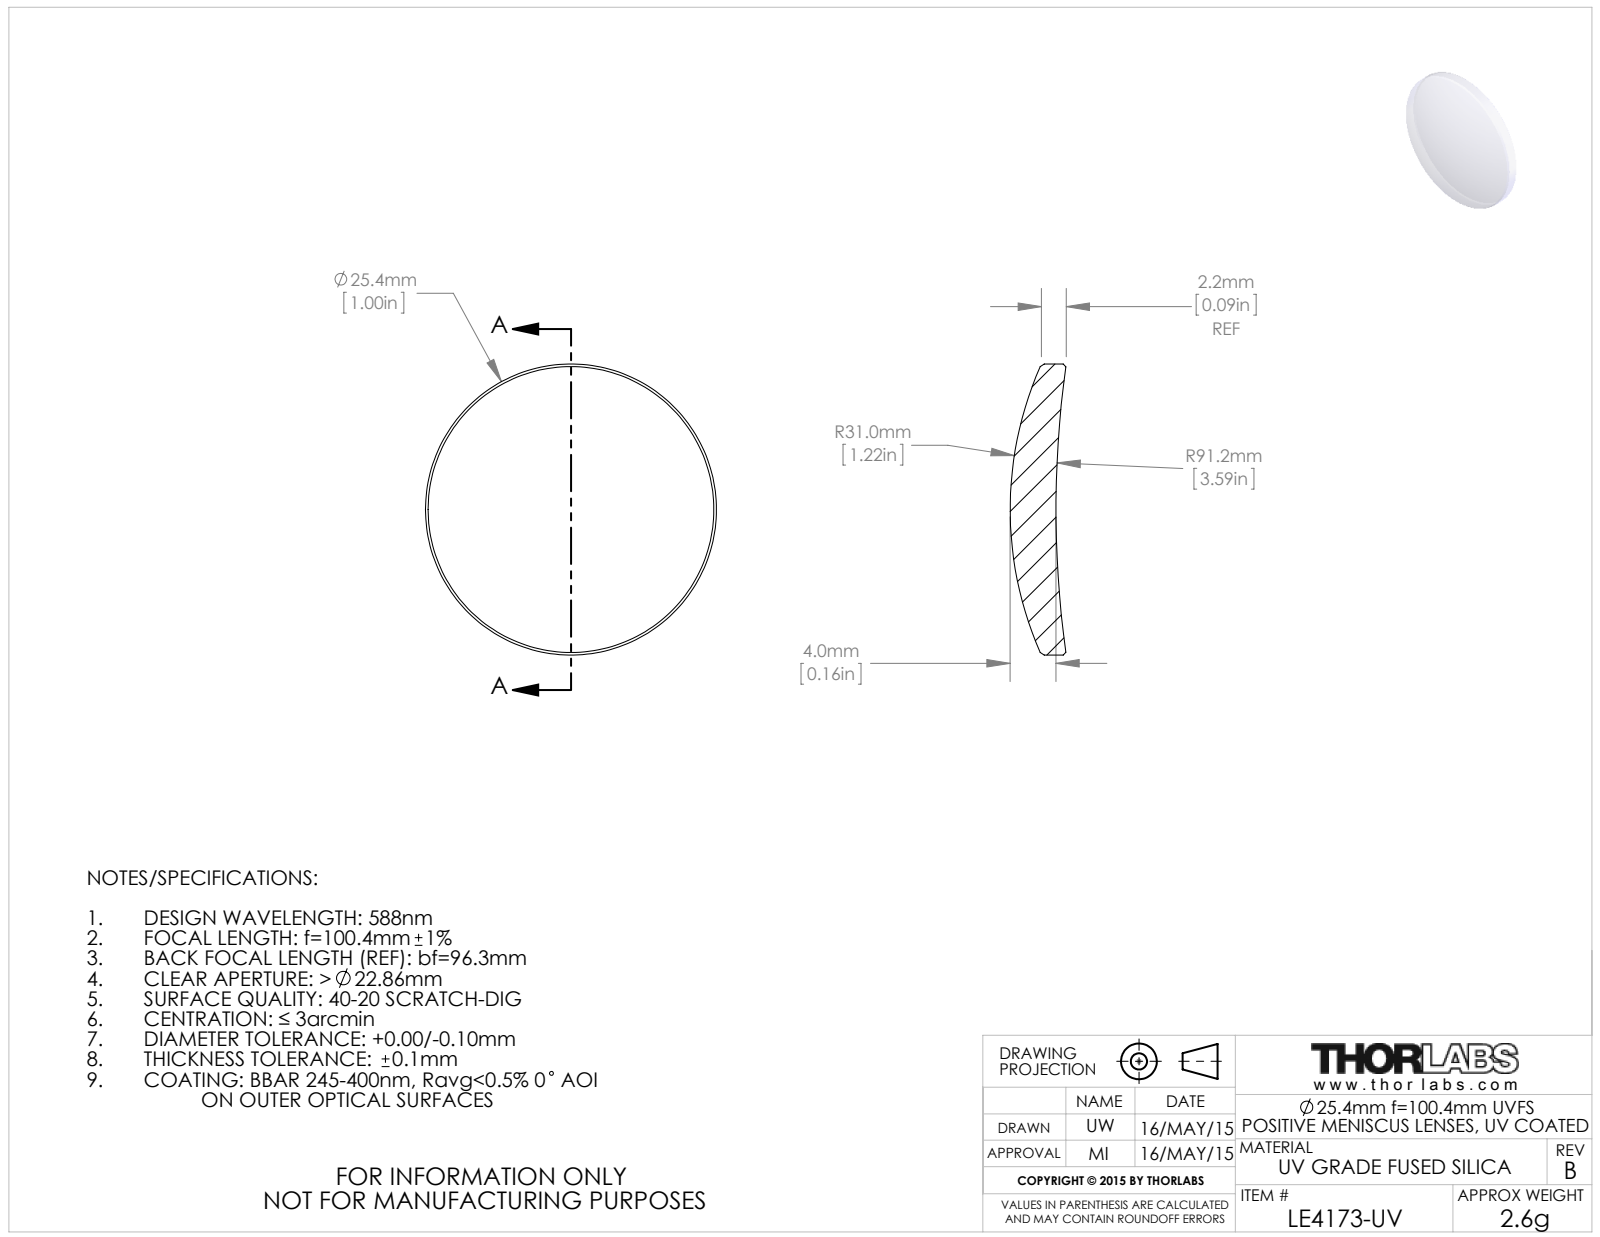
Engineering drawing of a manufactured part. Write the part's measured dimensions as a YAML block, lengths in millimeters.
part_name: "4925-E0W"
step_written_by: "SolidWorks 2014 (CONFIG_CONTROL_DESIGN)"
units: millimeters
bodies: {solids: 1, faces: 10, planar: 0, cylindrical: 2, other: 8}
overall_size: [25.4, 25.4, 4.85]
volume: 1568
surface_area: 1192
round_bosses_or_shafts:
  - {diameter: 25.4, count: 1}
